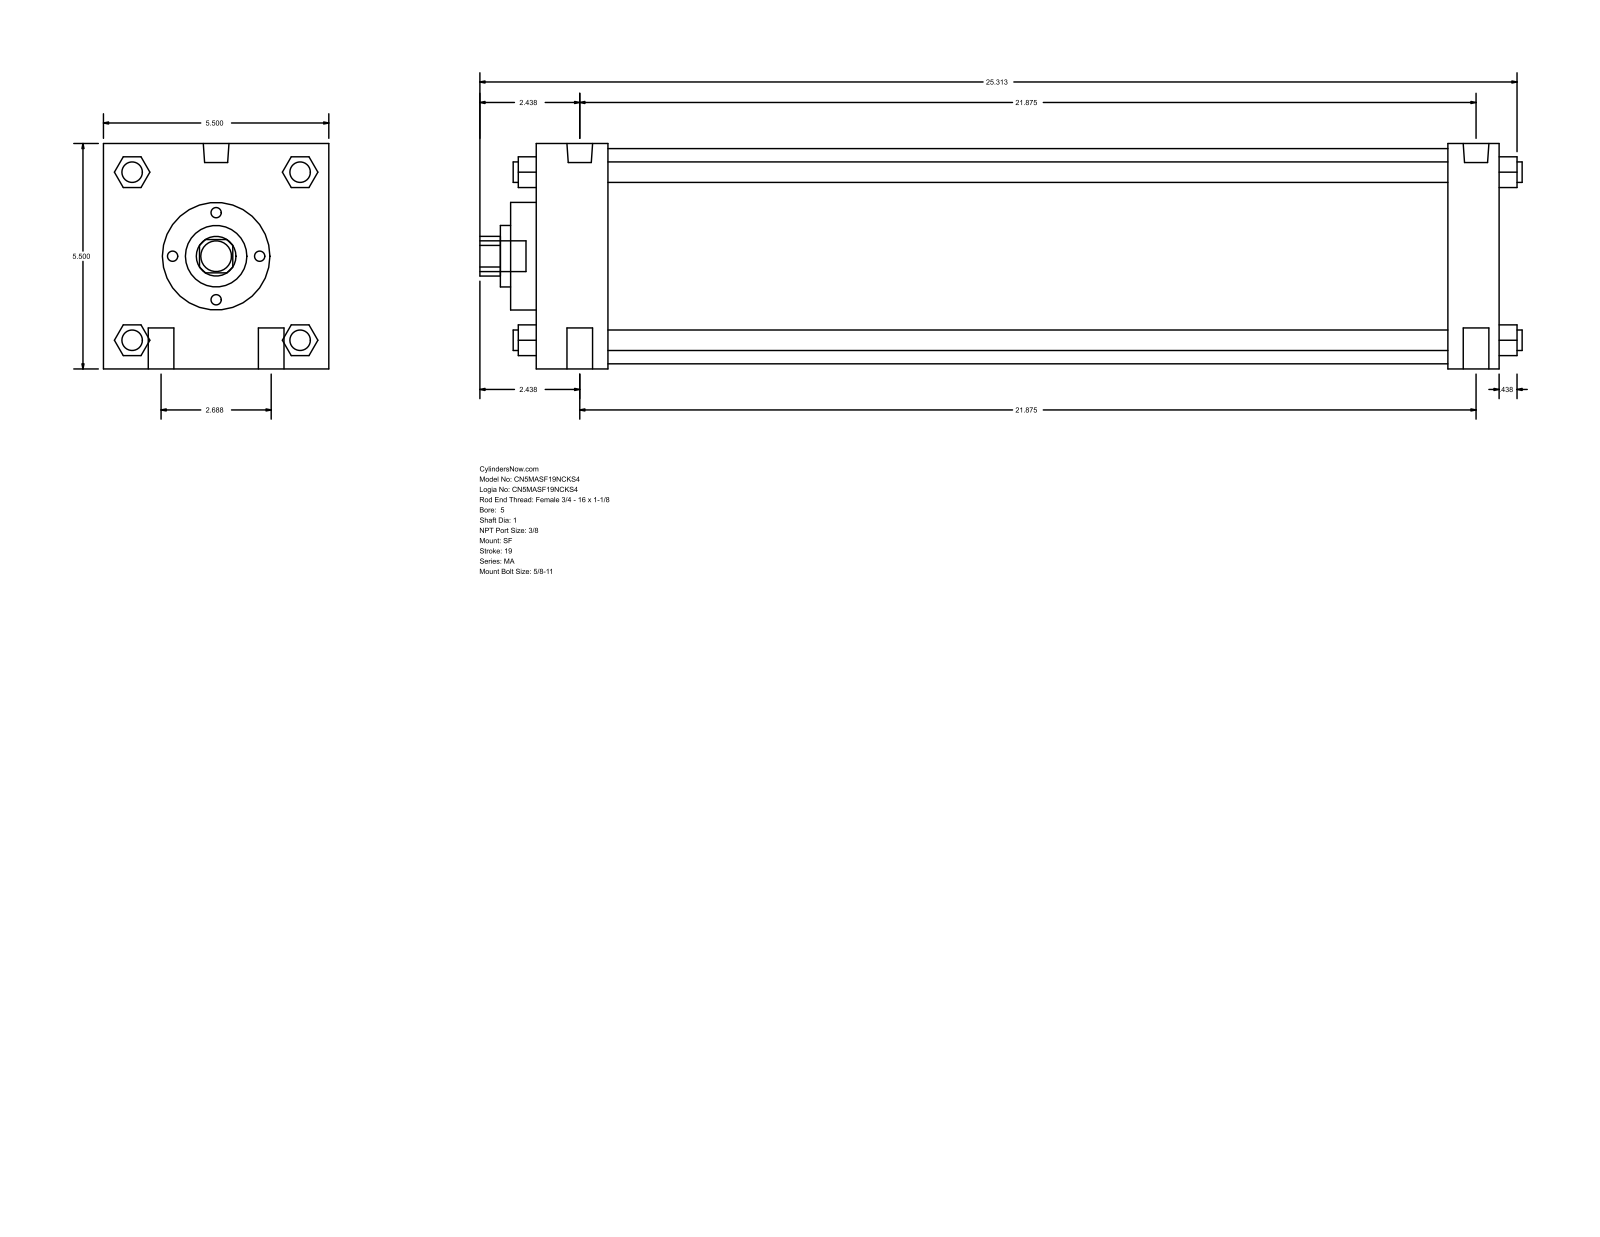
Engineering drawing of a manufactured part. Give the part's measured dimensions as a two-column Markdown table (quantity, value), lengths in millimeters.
| quantity | value |
| --- | --- |
| part name | MA_SF__0500_1 |
| STEP written by | GSSL Pune (CONFIG_CONTROL_DESIGN) |
| units | millimeters |
| bodies | 0 solids, 126 faces (95 planar, 31 cylindrical, 0 other) |
| overall size | 646.11 × 139.7 × 139.7 |
| round holes (diameter × count) | 25.4 × 1, 38.1 × 1, 66.67 × 1, 133.35 × 1 |
| round bosses / shafts (diameter × count) | 15.88 × 4, 12.7 × 4, 15.93 × 2, 11.11 × 2, 19.05 × 1 |
| partial cylindrical surfaces (radius × count) | 12.29 × 1 |
| main face-to-face distances | 139.7, 596.91, 44.46, 565.16, 520.7, 552.45, 31.75, 15.87, 60.33, 581.03 |
